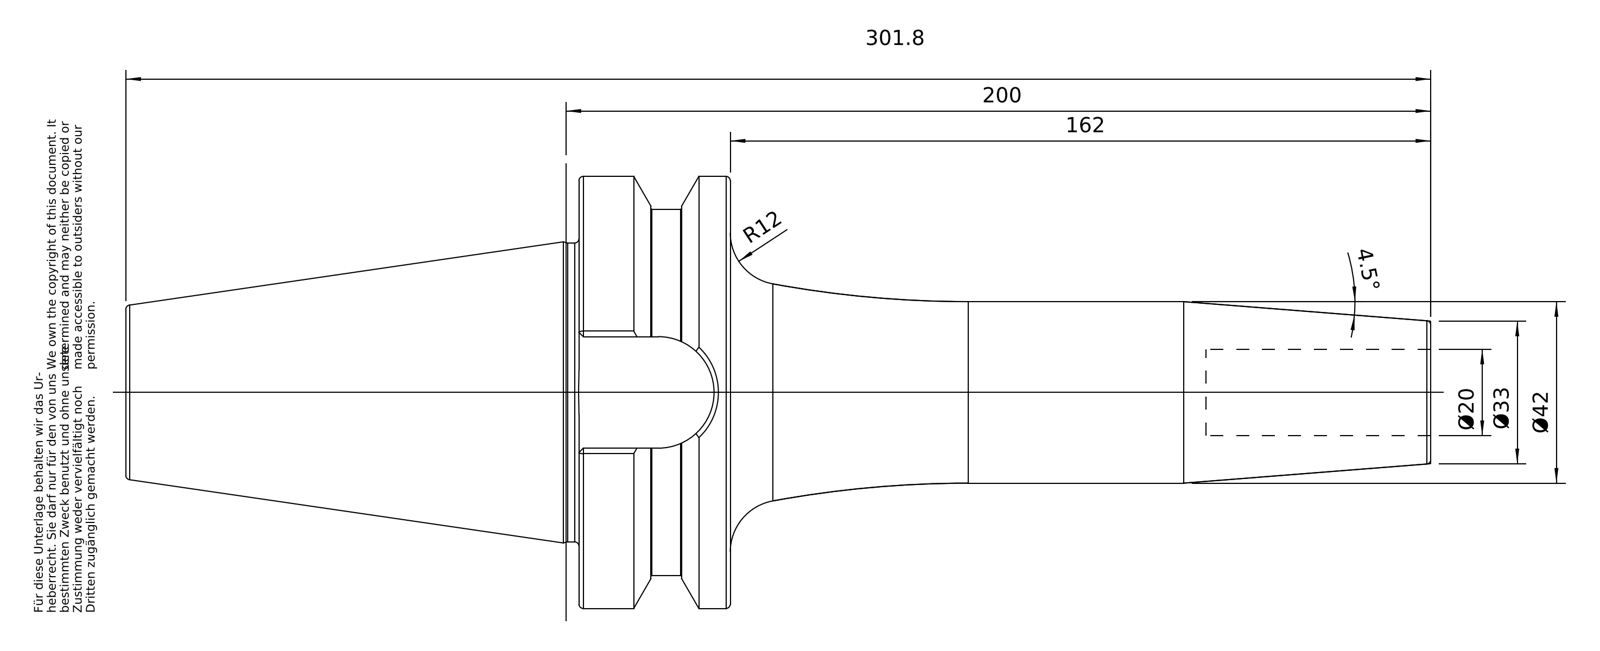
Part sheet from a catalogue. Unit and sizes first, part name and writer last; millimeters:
Units: millimetres
Overall size (bounding box): 301.8 × 99.97 × 99.97
Round holes (diameter × count): ⌀20 ×1, ⌀20.75 ×1, ⌀25.02 ×1, ⌀25.7 ×1
Round bosses / shafts (diameter × count): ⌀99.97 ×1, ⌀84.75 ×1, ⌀69.15 ×1, ⌀42 ×1, ⌀24.01 ×1
Partial cylindrical surfaces — rounded edges, fillets, slot ends (radius × count): R12.9 ×1
Main face-to-face distances: 35, 70.4, 104.8, 139.8, 301.8, 197, 162, 25.8, 249.8, 145
Volume: 679 887 mm³ · Surface area: 74 492 mm²
Bodies: 1 solid, 98 faces (26 planar, 22 cylindrical, 50 other)
Part name (STEP PRODUCT): 50-646-20
STEP written by: PRO/ENGINEER BY PARAMETRIC TECHNOLOGY CORPORATION, 2010430 (CONFIG_CONTROL_DESIGN)
